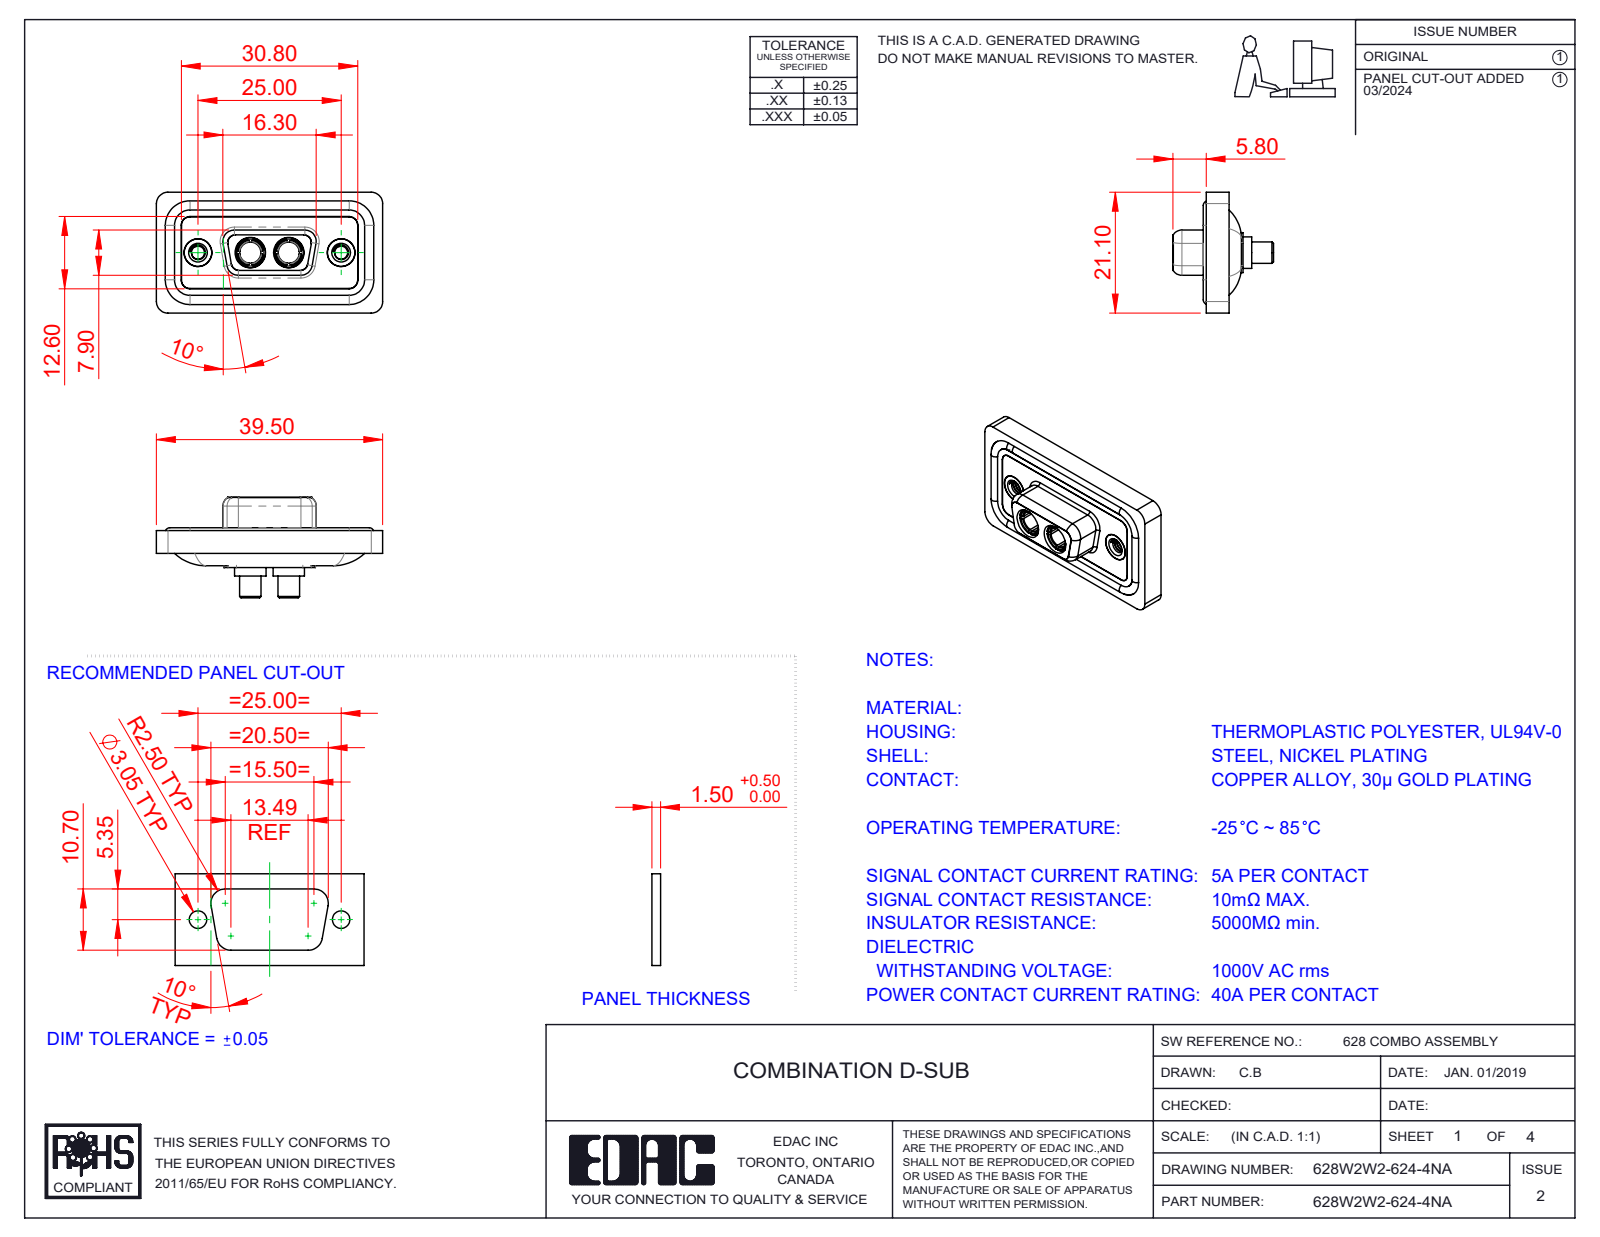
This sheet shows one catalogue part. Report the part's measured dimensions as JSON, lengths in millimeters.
{"part_name": "Power Socket_40A S; 628Combo Threaded Rivet_A; 628Combo Waterproof Housing_09 Contacts; 628Combo Shell Rear_09 Contacts (+3 more)", "step_written_by": "SolidWorks 2023 (CONFIG_CONTROL_DESIGN)", "units": "millimeters", "bodies": {"solids": 11, "faces": 532, "planar": 163, "cylindrical": 236, "other": 133}, "overall_size": [39.5, 21.1, 17.55], "volume_mm3": 4751, "surface_area_mm2": 7655, "round_holes": [[4.85, 4], [2.26, 2], [3.7, 2], [4, 2], [4.05, 2], [5, 2], [5.3, 2]], "round_bosses_or_shafts": [[1.6, 4], [5.5, 2], [5.2, 2], [4.96, 2], [4.95, 2], [4.8, 2], [4.75, 2], [3.75, 2]], "partial_cylinders_radius": [[1.5, 22], [2, 18], [1.35, 8], [1.6, 8], [0.25, 4], [0.5, 4], [0.6, 4], [0.65, 4]], "face_to_face_distances": [0.4, 1.8, 1.1, 2.9, 0.5, 1.6, 5.65, 7.45, 5.35, 3.1], "hole_center_spacings": [9.14, 15.86, 6.72, 25]}
